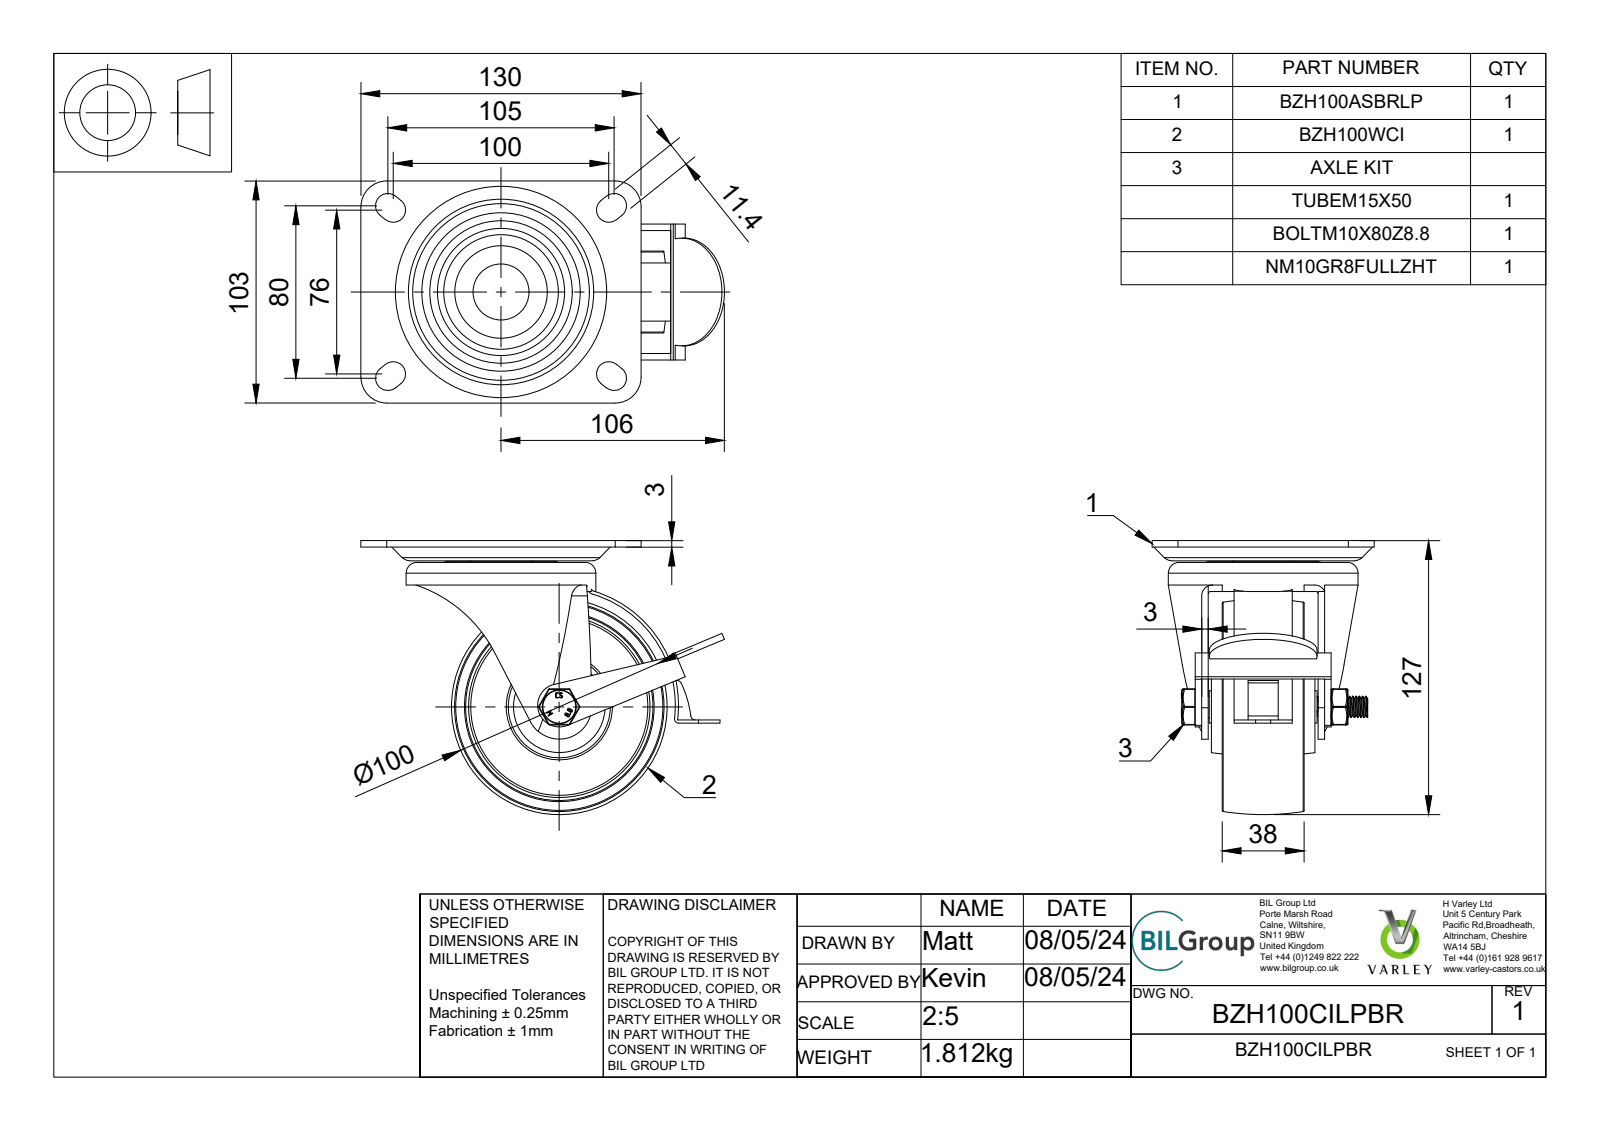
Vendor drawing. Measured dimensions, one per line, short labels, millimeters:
name: BZH100CILPBR v3; BZH100ASBRLP v1; ZINC PLATED, PRESSED STEEL TOP PLATE; ZINC PLATED, PRESSED STEEL FORKS (+8 more)
written by: Autodesk Translation Framework v12.20.1.177 (AUTOMOTIVE_DESIGN)
unit: mm
bodies: 9 solids, 406 faces (144 planar, 127 cylindrical, 135 other)
size: 168.66 × 127.13 × 103
volume: 287 590 mm³; area: 127 226 mm²
holes: 1× ⌀10, 1× ⌀10.5, 1× ⌀15.2, 1× ⌀30, 1× ⌀82
bosses: 1× ⌀88, 1× ⌀36, 1× ⌀28, 1× ⌀26, 1× ⌀16, 1× ⌀15, 1× ⌀9.85, 1× ⌀8.14
rounds: 8× R2, 8× R5.7, 6× R0.5, 4× R0.33, 4× R0.64, 4× R12, 3× R10, 2× R0.63
face distances: 3, 5, 21.5, 26, 57, 31, 4.5, 26.5, 23, 54
